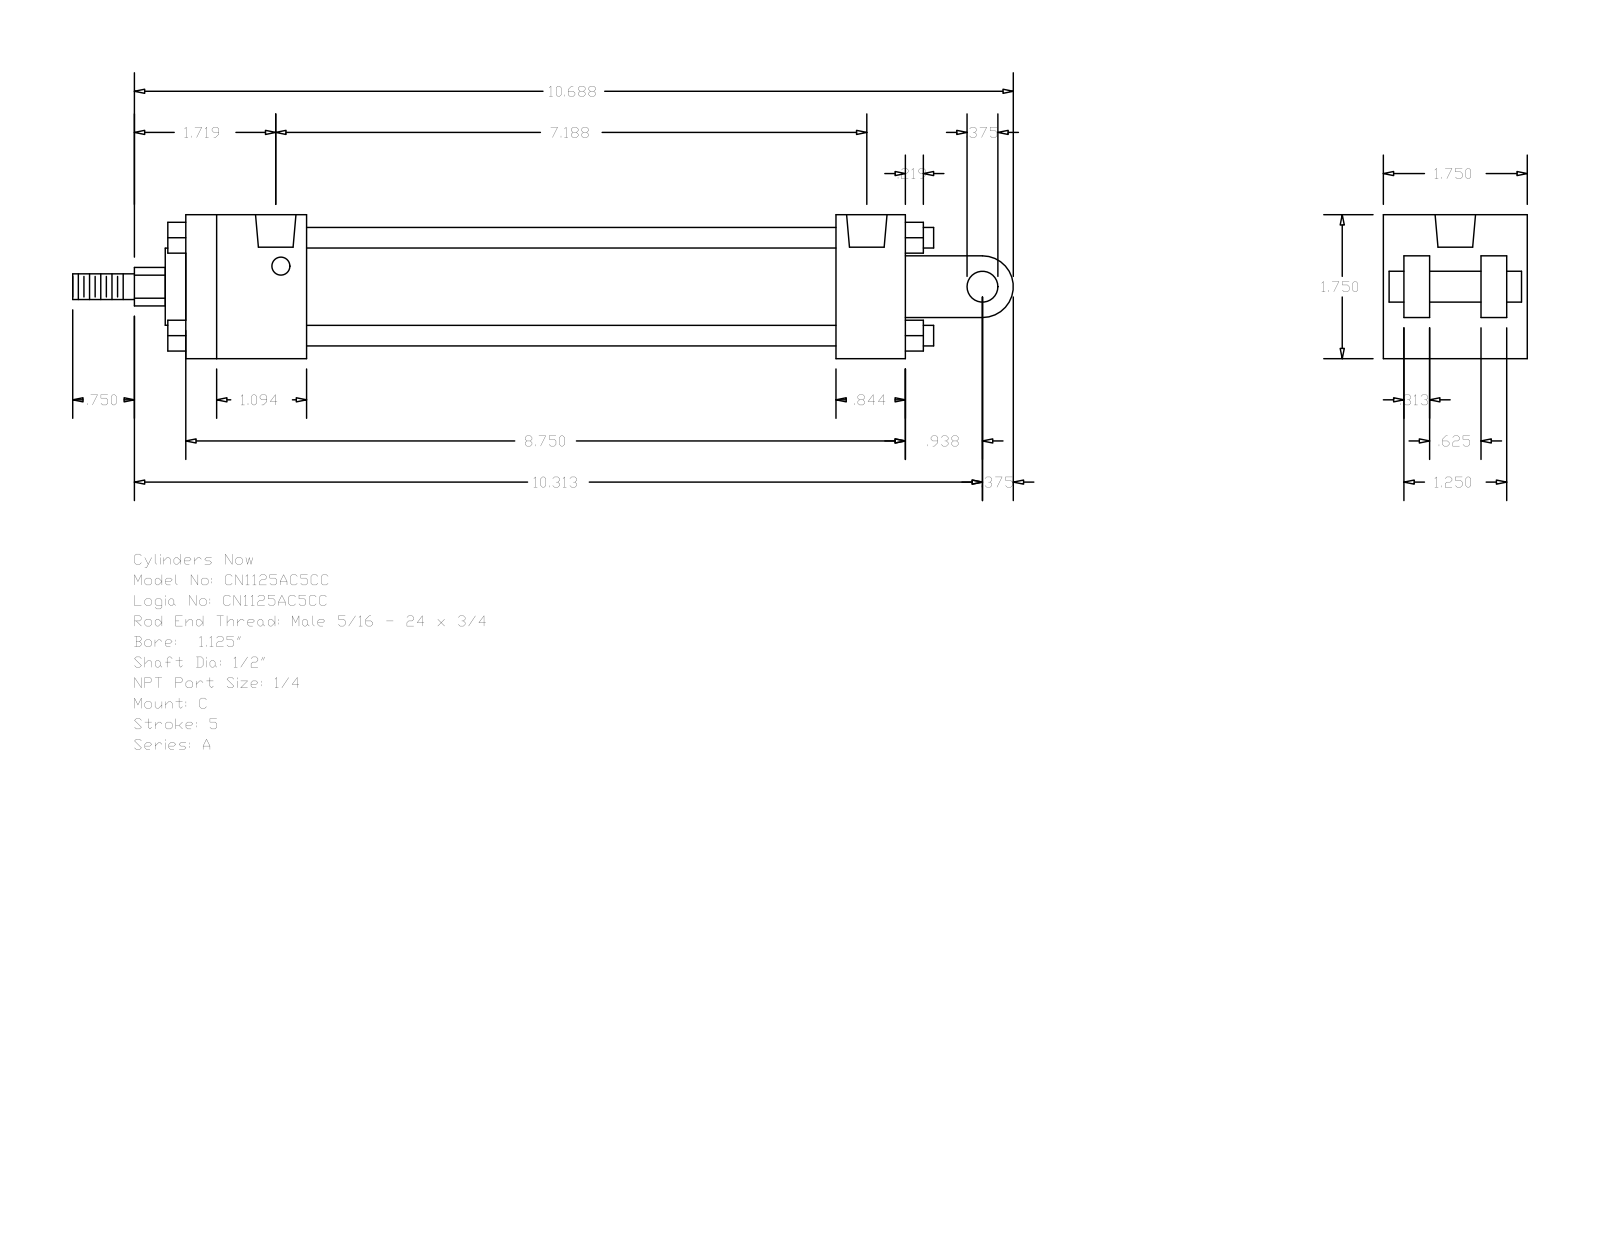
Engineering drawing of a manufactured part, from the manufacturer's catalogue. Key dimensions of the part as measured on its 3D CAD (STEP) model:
Part name (STEP PRODUCT): A_C__0112_0.5
STEP written by: GSSL Pune (CONFIG_CONTROL_DESIGN)
Units: millimetres
Bodies: 0 solids, 135 faces (102 planar, 33 cylindrical, 0 other)
Overall size (bounding box): 290.51 × 44.45 × 44.45
Round holes (diameter × count): ⌀5.56 ×4, ⌀12.49 ×2
Round bosses / shafts (diameter × count): ⌀6.35 ×4, ⌀31.88 ×1, ⌀23.81 ×1, ⌀12.7 ×1, ⌀9.53 ×1, ⌀7.94 ×1
Partial cylindrical surfaces — rounded edges, fillets, slot ends (radius × count): R5.94 ×1, R9.53 ×1
Main face-to-face distances: 44.46, 6.35, 31.76, 14.29, 222.24, 30.17, 200.81, 21.43, 37.3, 163.51
Hole centre spacings: 179.39, 1.58, 1.59, 180.97, 180.98, 182.56
